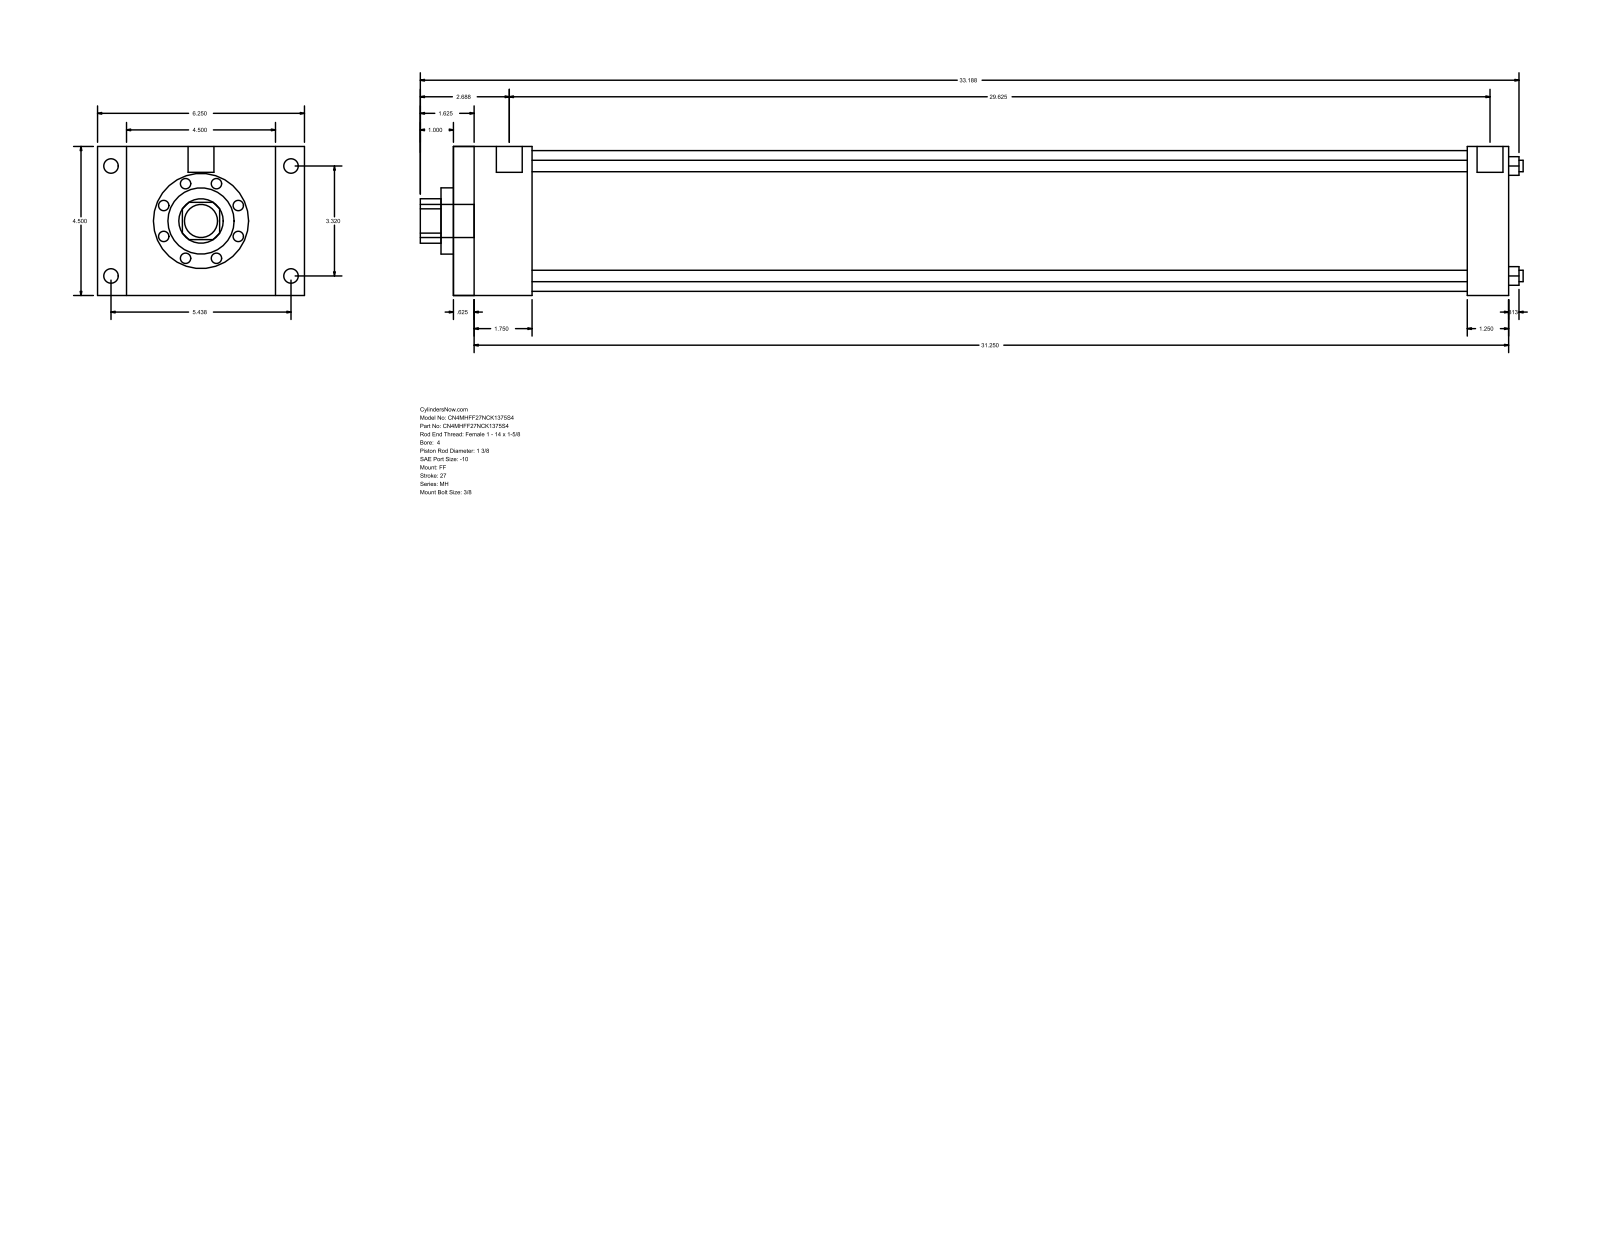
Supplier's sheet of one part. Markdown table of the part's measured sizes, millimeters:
| quantity | value |
| --- | --- |
| part name | MH_FF__0400_1.375 |
| STEP written by | GSSL Pune (CONFIG_CONTROL_DESIGN) |
| units | millimeters |
| bodies | 0 solids, 92 faces (64 planar, 28 cylindrical, 0 other) |
| overall size | 846.14 × 158.75 × 114.3 |
| round holes (diameter × count) | 8.76 × 4, 34.92 × 1, 50.8 × 1, 107.95 × 1 |
| round bosses / shafts (diameter × count) | 11.13 × 4, 8.73 × 4, 19.84 × 2, 25.4 × 1 |
| partial cylindrical surfaces (radius × count) | 17.06 × 1 |
| main face-to-face distances | 114.3, 809.62, 15.87, 793.75, 60.32, 44.45, 749.3, 777.87, 762, 717.55 |
| hole center spacings | 59.62, 84.32, 119.25 |
